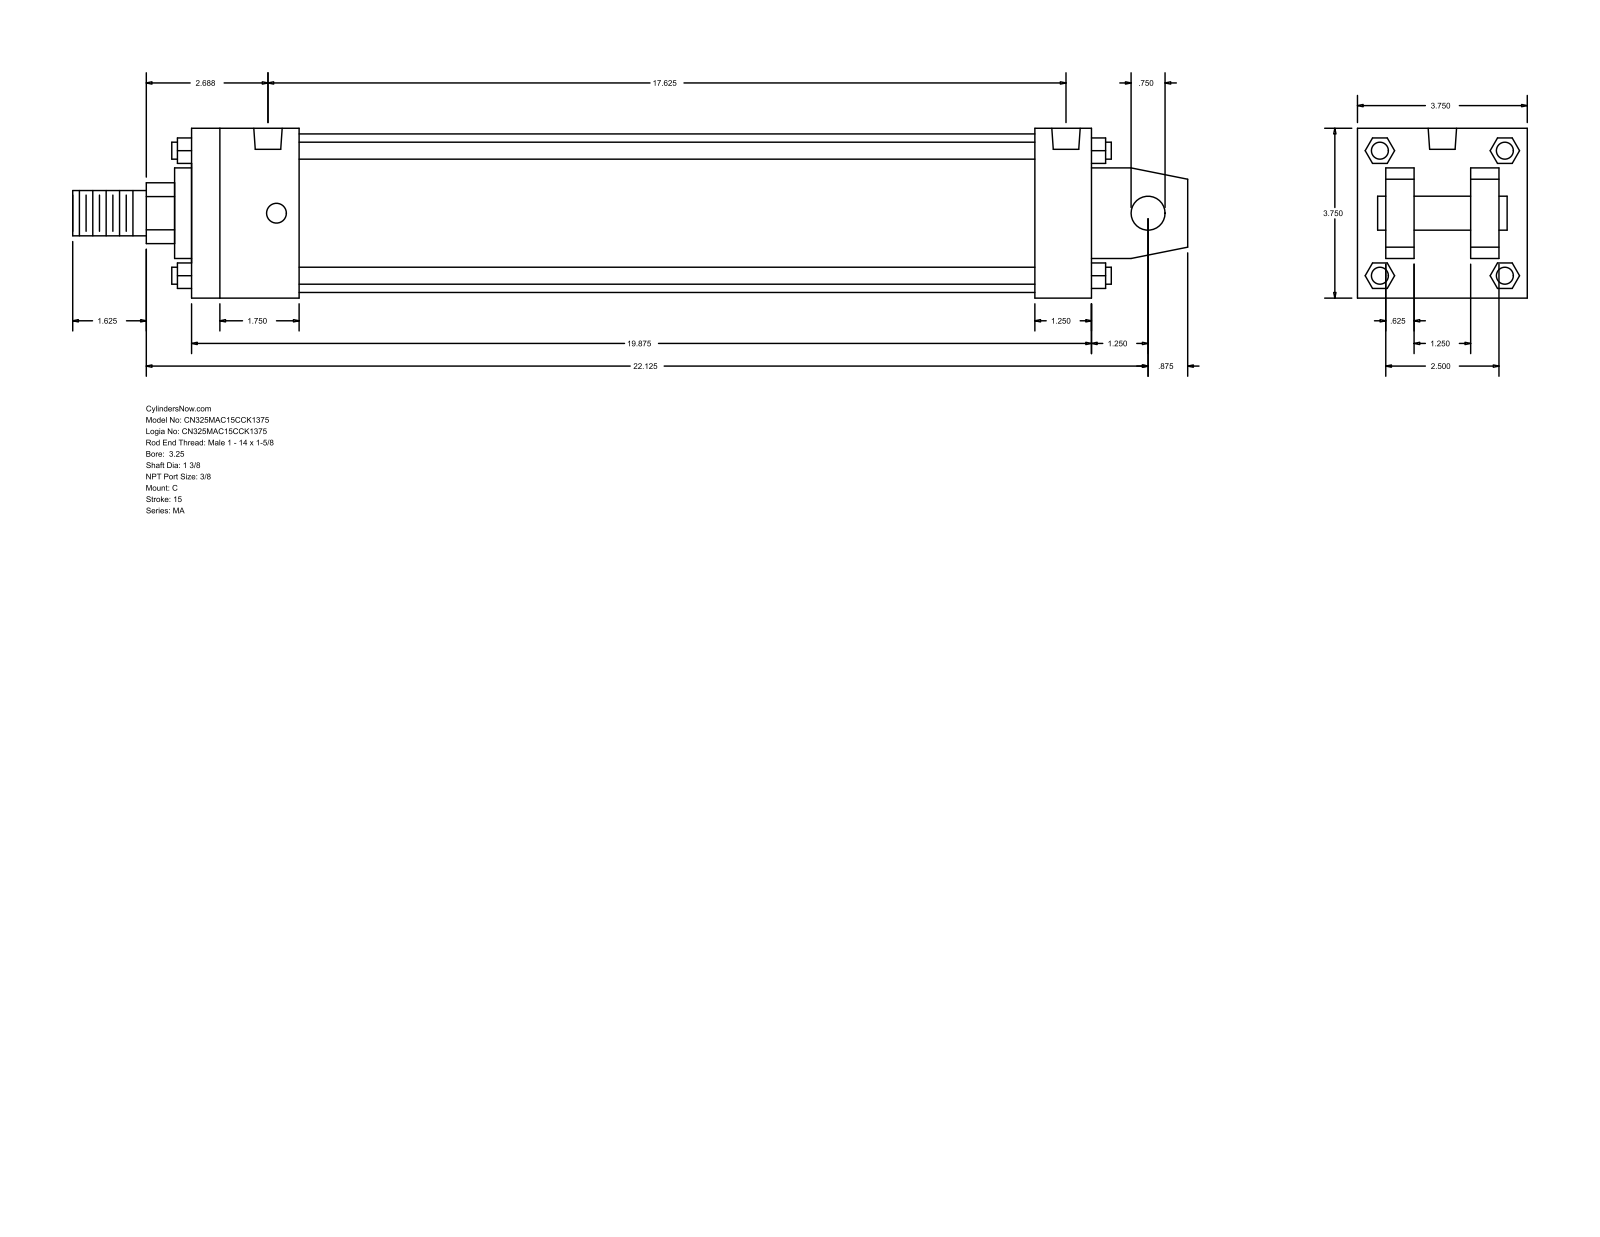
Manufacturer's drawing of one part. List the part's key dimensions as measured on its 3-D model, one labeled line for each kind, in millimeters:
Part name (STEP PRODUCT): MA_C__0325_1.375
STEP written by: GSSL Pune (CONFIG_CONTROL_DESIGN)
Units: millimetres
Bodies: 0 solids, 139 faces (108 planar, 31 cylindrical, 0 other)
Overall size (bounding box): 625.48 × 95.25 × 95.25
Round holes (diameter × count): ⌀11.11 ×4, ⌀15.93 ×2
Round bosses / shafts (diameter × count): ⌀9.53 ×4, ⌀88.9 ×1, ⌀50.8 ×1, ⌀34.92 ×1, ⌀25.4 ×1, ⌀19.05 ×1
Partial cylindrical surfaces — rounded edges, fillets, slot ends (radius × count): R17.06 ×1
Main face-to-face distances: 95.24, 15.87, 63.5, 504.83, 31.74, 79.37, 47.63, 473.08, 31.75, 60.32
Hole centre spacings: 438.15, 4.76, 4.77, 442.91, 442.92, 447.68
